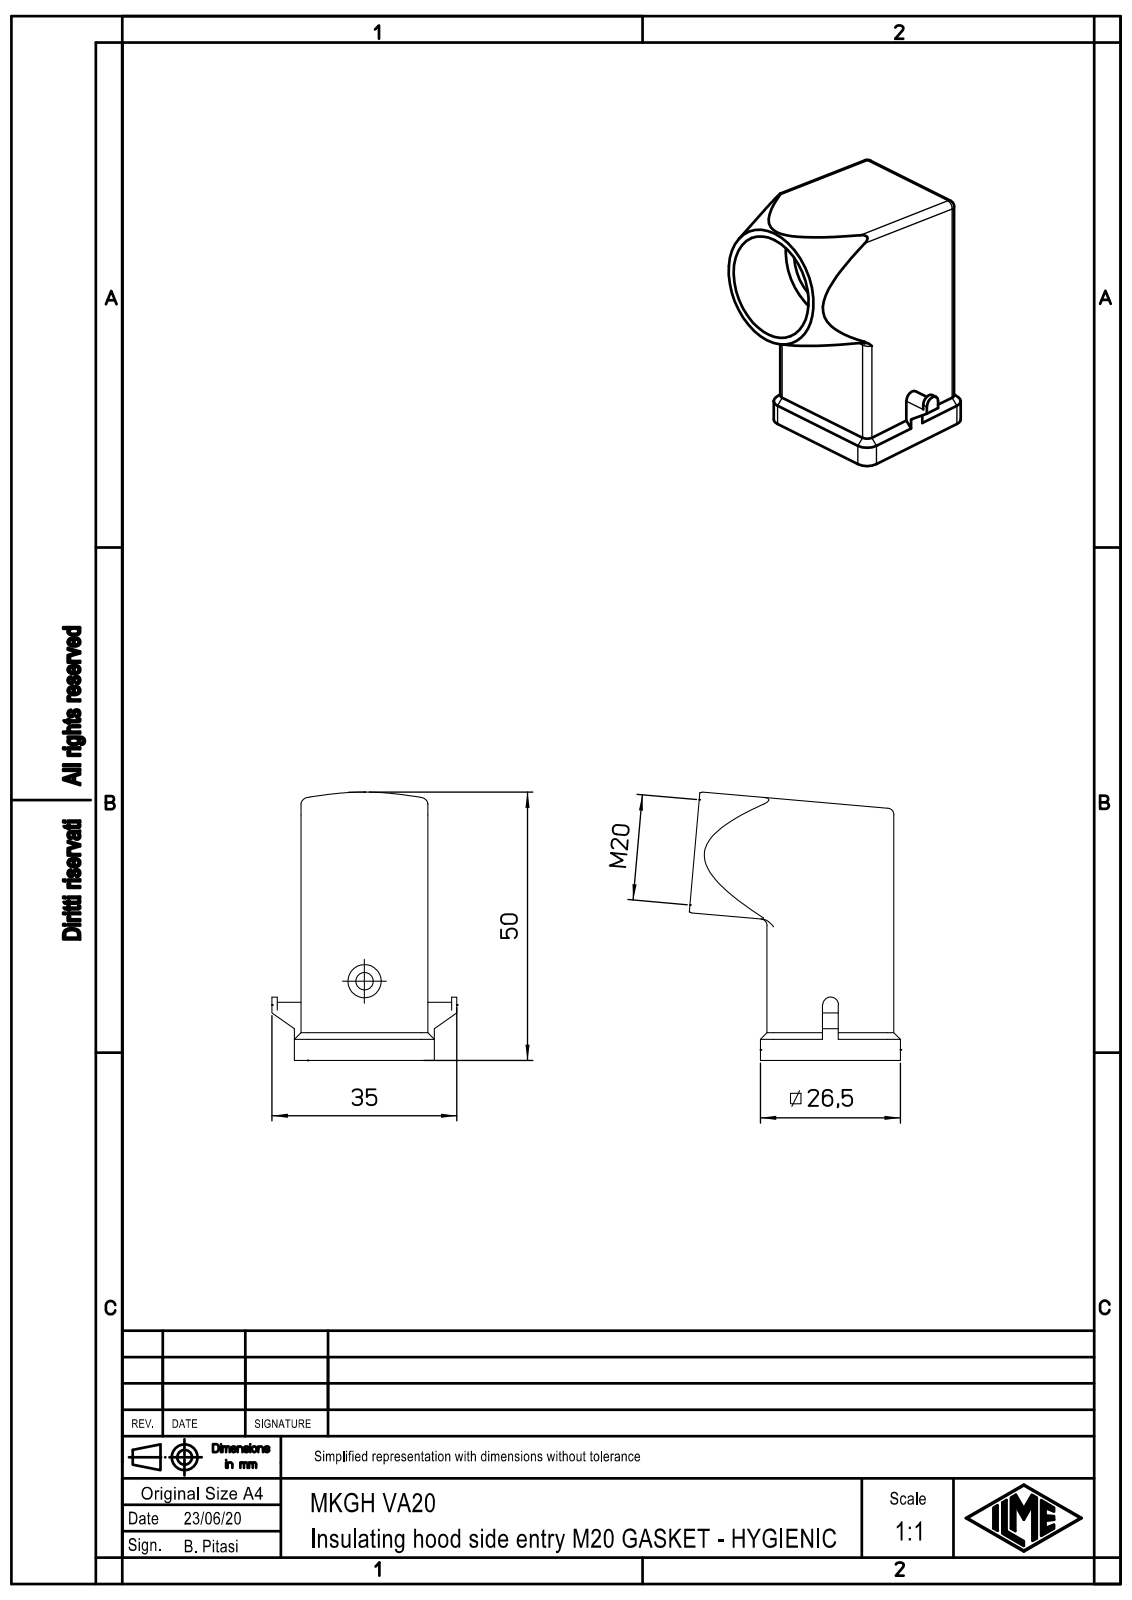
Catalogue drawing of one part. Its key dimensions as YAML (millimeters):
part_name: "MKGH VA20"
step_written_by: "Creo Elements/Direct Modeling 20.1B 02-Apr-2019 (C) Parametric Technology GmbH (AUTOMOTIVE_DESIGN)"
units: millimeters
bodies: {solids: 1, faces: 156, planar: 91, cylindrical: 52, other: 13}
overall_size: [50.84, 39.96, 35]
volume: 9970
surface_area: 12015
round_holes:
  - {diameter: 3.3, count: 1}
  - {diameter: 15.5, count: 1}
  - {diameter: 20, count: 1}
partial_cylinders:
  - {radius: 0.25, count: 14}
  - {radius: 1.25, count: 8}
  - {radius: 1.75, count: 8}
  - {radius: 2.5, count: 4}
  - {radius: 1.5, count: 2}
face_to_face_distances: [1.25, 22.75, 24, 21.5, 2.5, 25.25, 23, 5, 26.5, 13.25]
